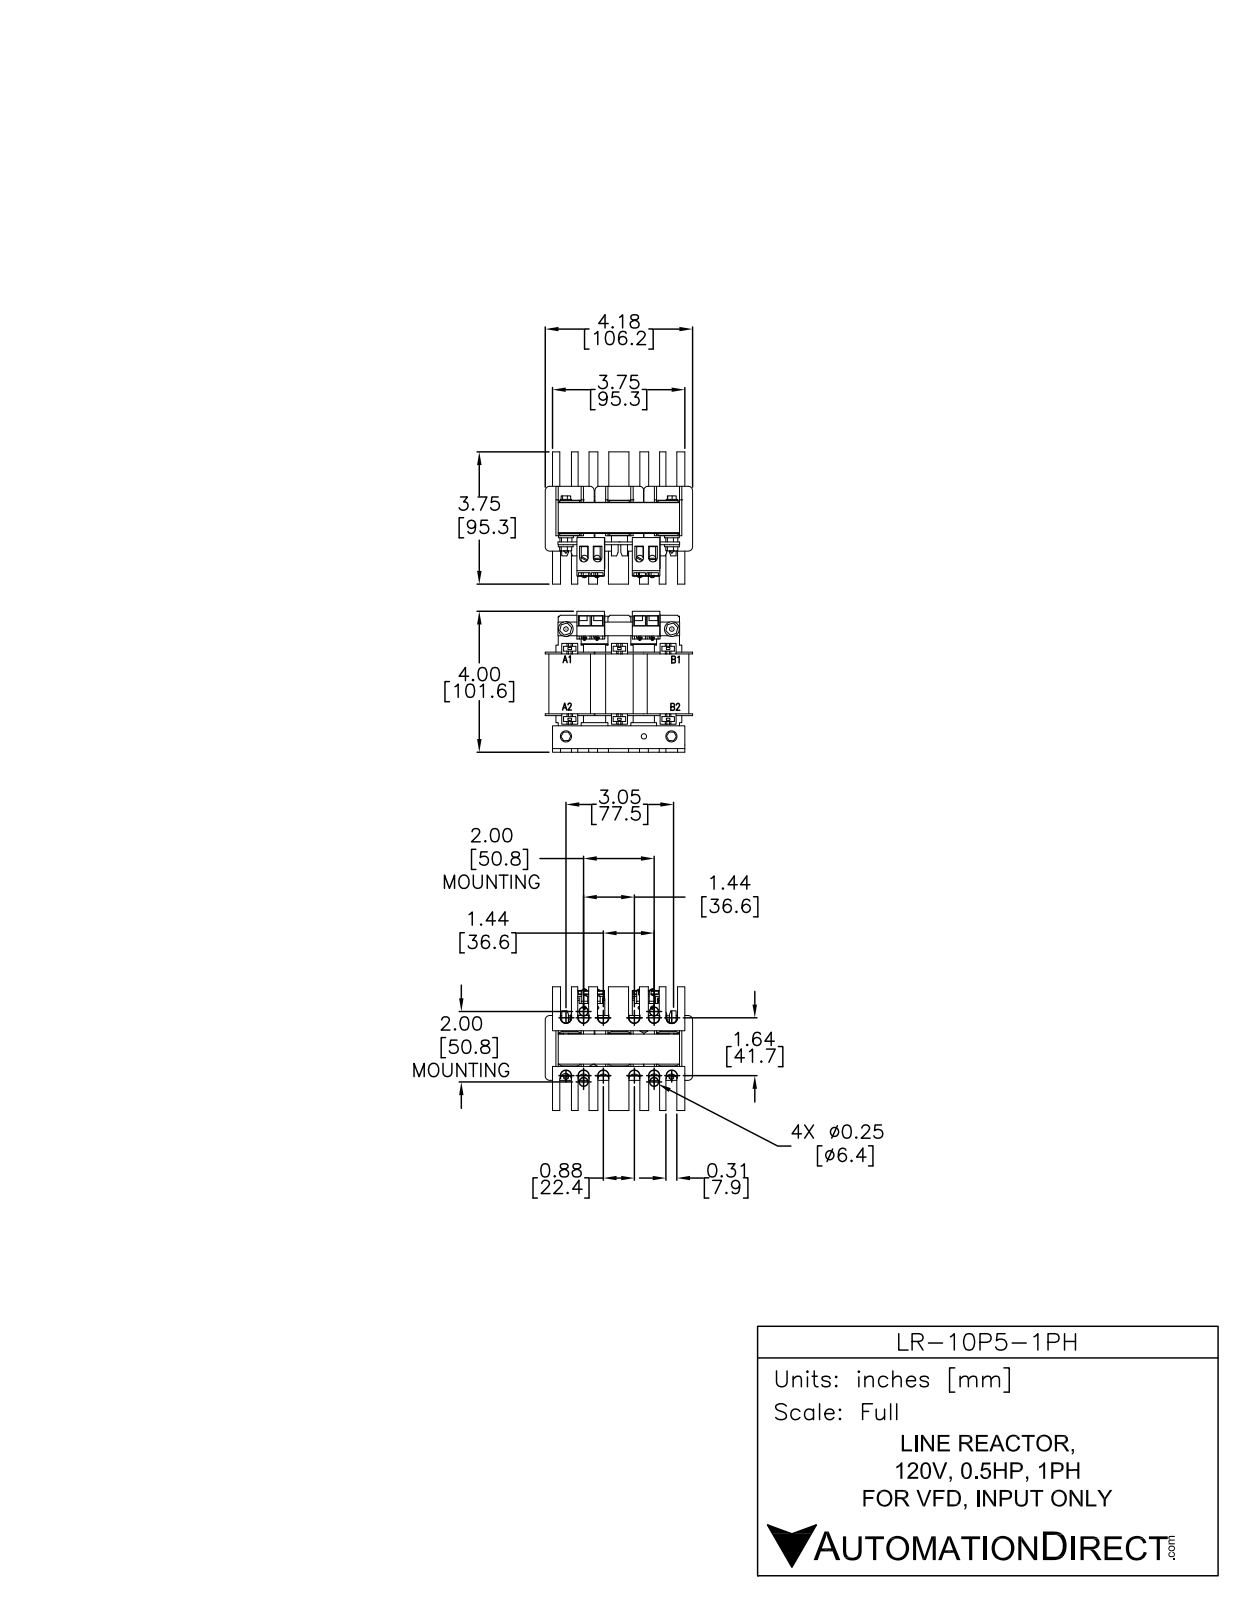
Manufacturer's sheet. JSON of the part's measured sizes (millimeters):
{"part_name": "LR-10P5-1PH", "step_written_by": "SolidWorks 2011 (AUTOMOTIVE_DESIGN)", "units": "millimeters", "bodies": {"solids": 17, "faces": 1066, "planar": 846, "cylindrical": 220, "other": 0}, "overall_size": [105.25, 98.41, 89.25], "volume_mm3": 290384, "surface_area_mm2": 108495, "round_bosses_or_shafts": [[7.75, 4], [3.5, 4]], "partial_cylinders_radius": [[4, 42], [1.82, 24], [8, 12], [1, 8], [3, 4], [0.86, 3], [1.25, 2]], "face_to_face_distances": [5, 26.25, 2.5, 7.5, 51, 48.5, 43.5, 2.75, 21.5, 2]}
